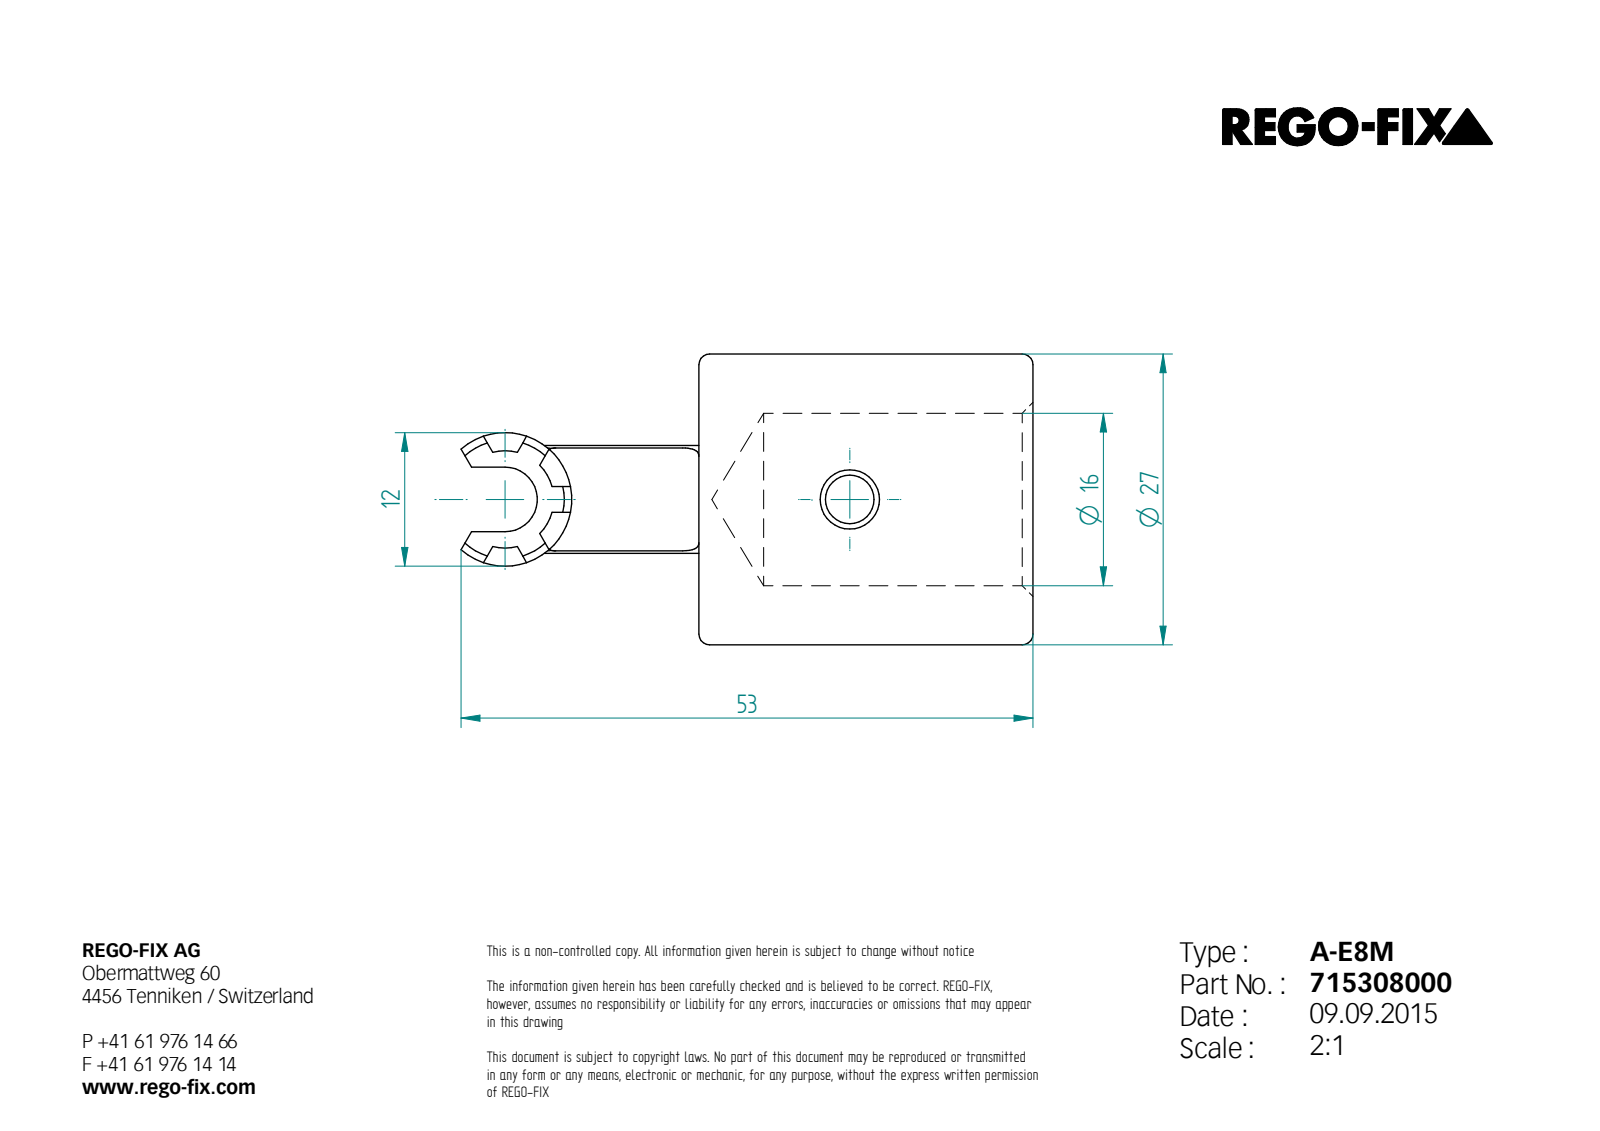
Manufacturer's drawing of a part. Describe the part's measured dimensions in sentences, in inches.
Its 3-D file was written by "Unknown (AUTOMOTIVE_DESIGN)". It is 1 solid with 43 faces: 25 planar, 11 cylindrical and 7 other. Overall it measures 2.09 by 1.063 by 1.063 inches. Its volume is 0.782 cubic inches and its surface area 8.967 square inches. Round holes: 1 of diameter 0.177, 1 of diameter 0.217, 1 of diameter 0.63. Round bosses or shafts: 1 of diameter 1.063. Partial cylindrical surfaces (rounded edges, fillets, slot ends): 2 of radius 0.059, 1 of radius 0.118, 1 of radius 0.197, 1 of radius 0.244. The main face-to-face distances are 1.22, 0.118, 0.209, 0.091, 0.094, 0.315, 0.197, 0.106, 0.236, 0.071.
